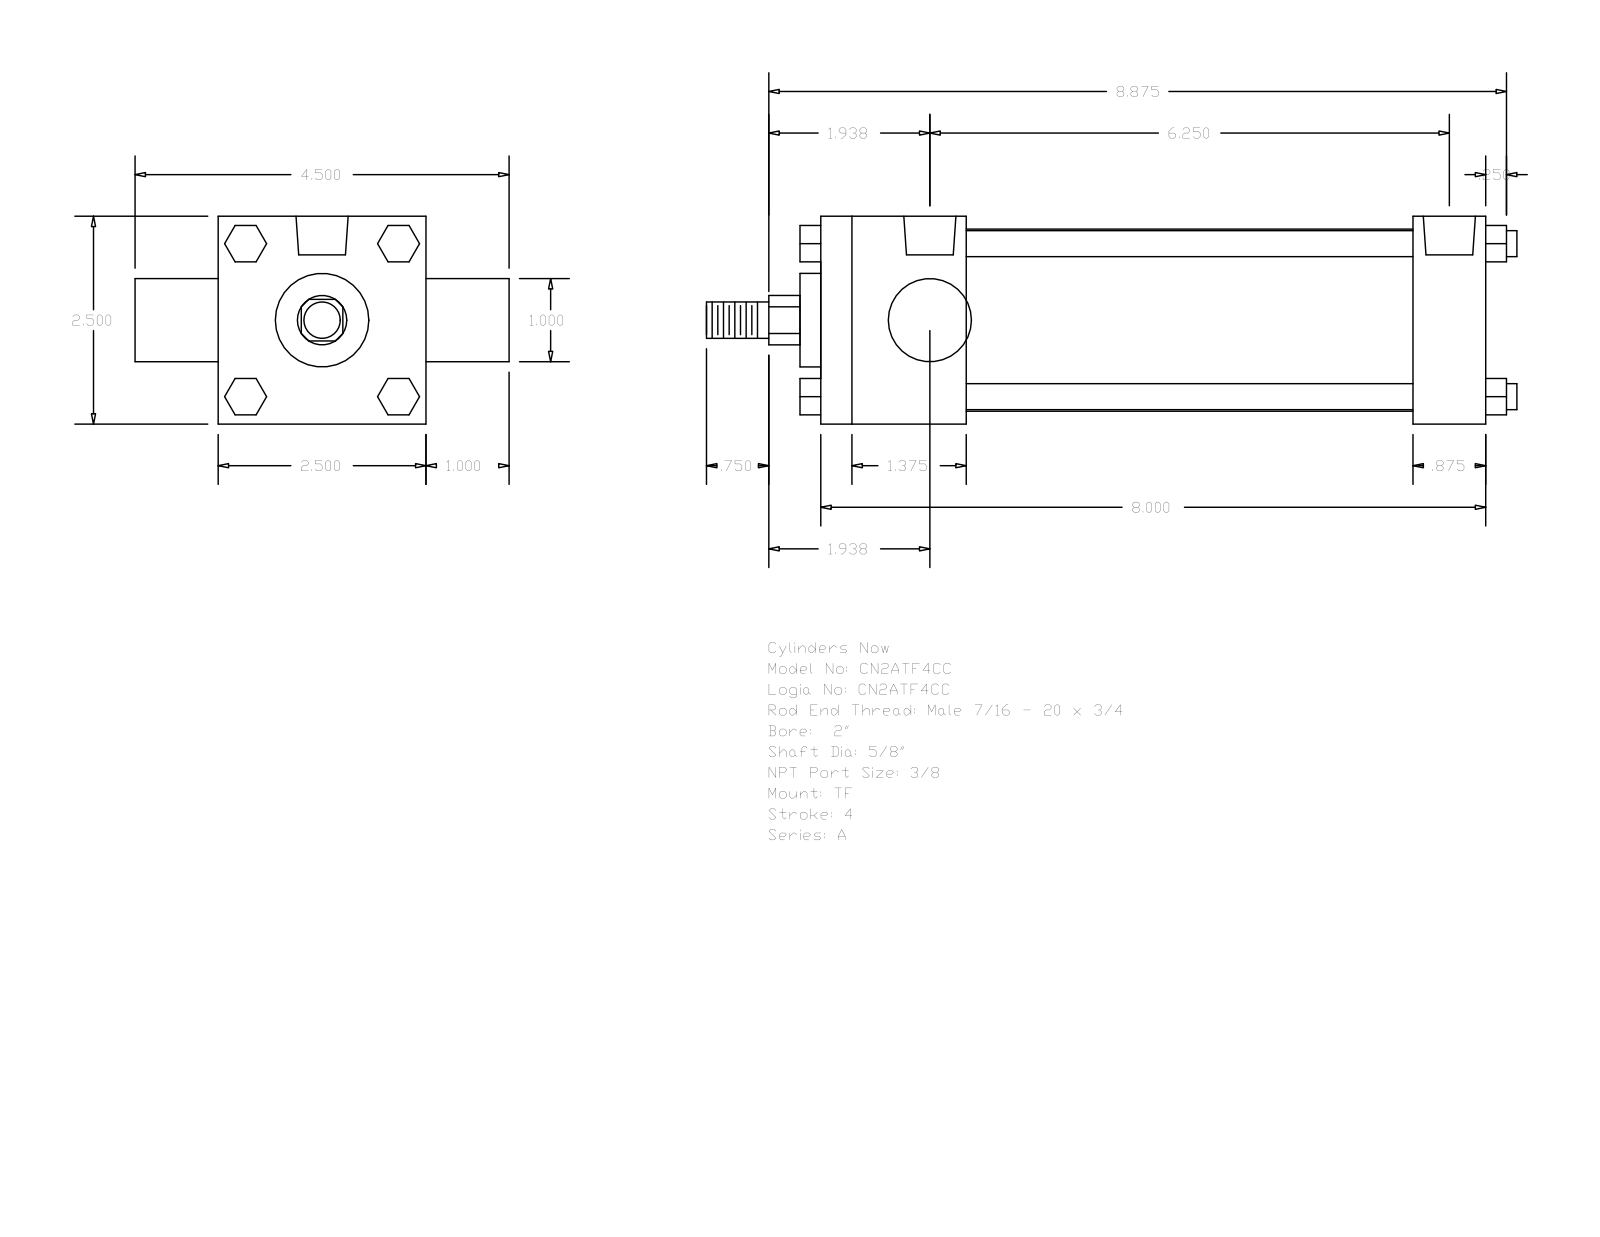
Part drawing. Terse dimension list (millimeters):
name: A_TF__0200_0.625
written by: GSSL Pune (CONFIG_CONTROL_DESIGN)
unit: mm
bodies: 0 solids, 120 faces (92 planar, 28 cylindrical, 0 other)
size: 247.65 × 114.3 × 63.5
holes: 3× ⌀5.56, 2× ⌀15.93
bosses: 4× ⌀7.94, 1× ⌀55.63, 1× ⌀28.57, 1× ⌀25.4, 1× ⌀15.88, 1× ⌀11.11
rounds: 1× R7.54
face distances: 63.5, 203.19, 44.45, 180.97, 136.52, 158.74, 22.22, 25.4, 88.9, 50.8
hole spacings: 3.97, 3.98, 150.8, 154.77, 154.78, 158.75
